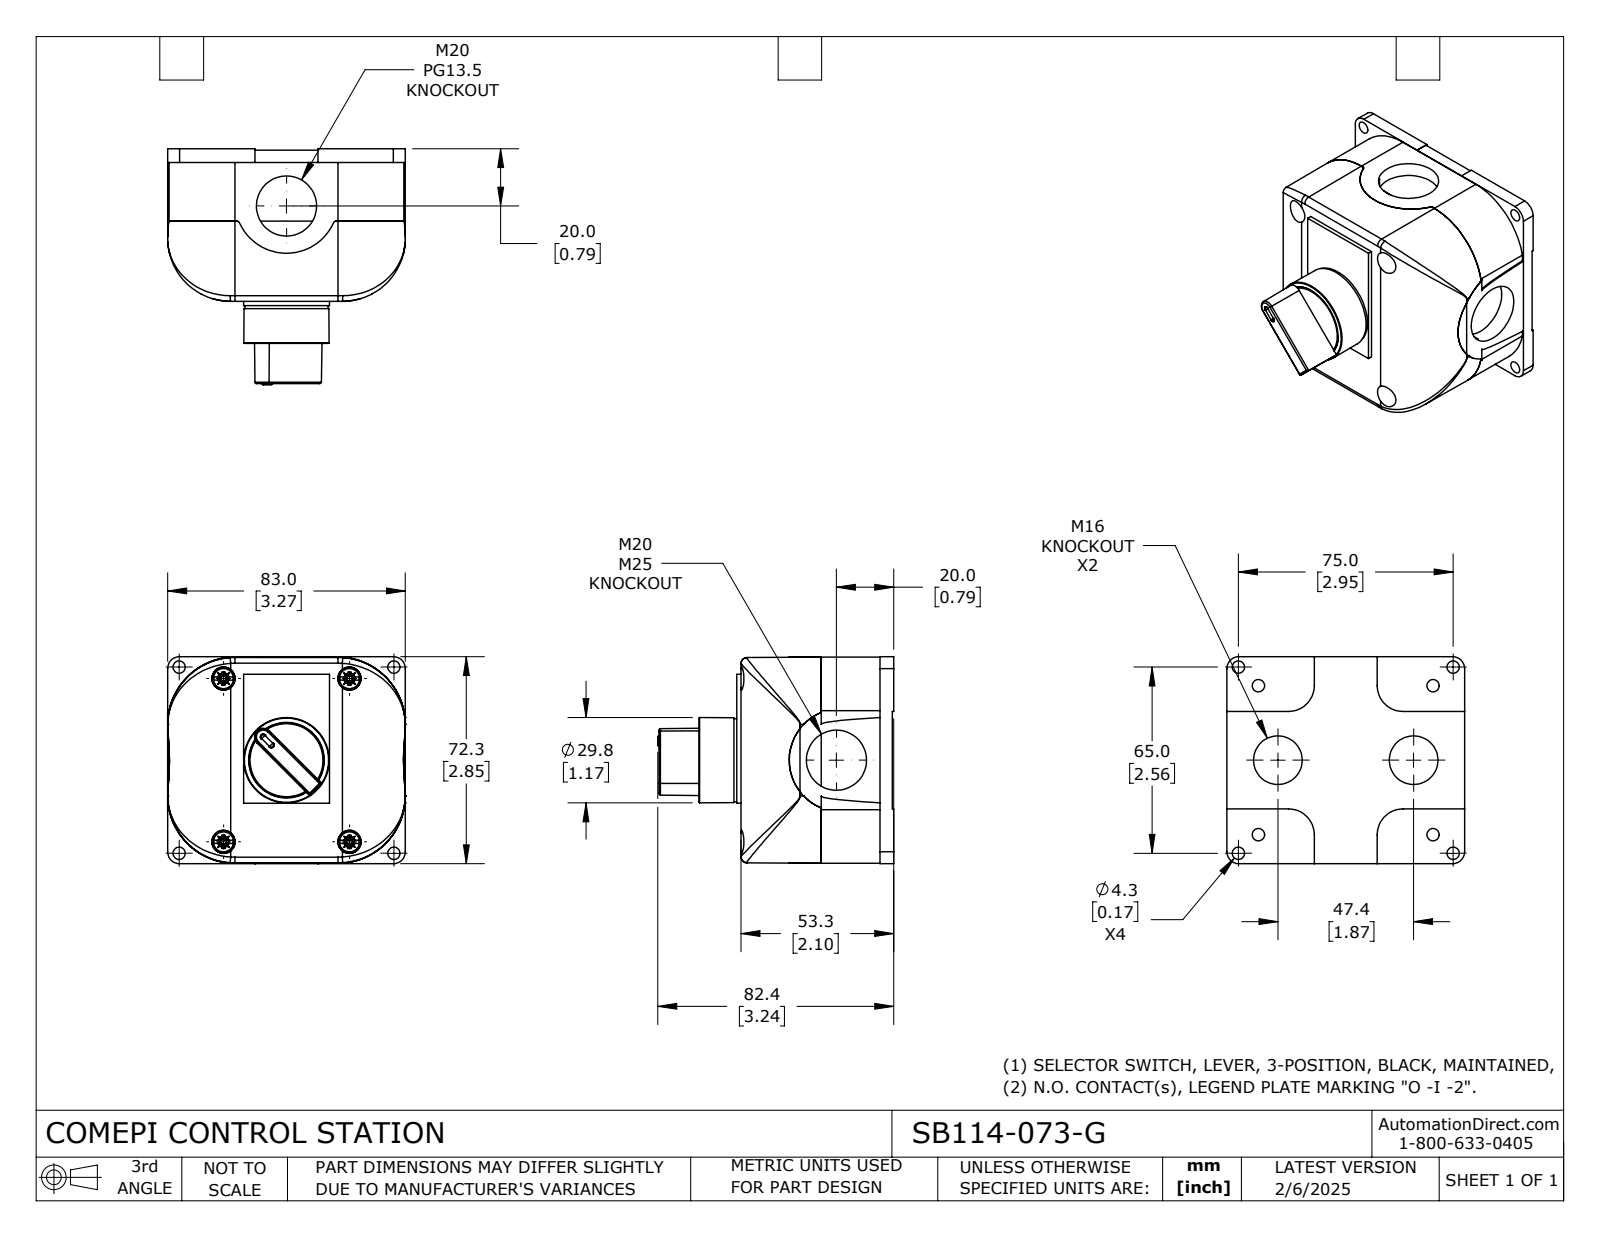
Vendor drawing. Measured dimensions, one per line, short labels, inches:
name: SB114-073-G
written by: SolidWorks 2024 (CONFIG_CONTROL_DESIGN)
unit: in
bodies: 5 solids, 586 faces (332 planar, 159 cylindrical, 95 other)
size: 3.268 × 3.244 × 2.846
volume: 13.1 in³; area: 94.77 in²
holes: 8× ⌀0.169, 4× ⌀0.323, 2× ⌀0.669, 2× ⌀0.827, 1× ⌀0.098, 1× ⌀0.5, 1× ⌀0.551, 1× ⌀0.75, 1× ⌀0.854, 1× ⌀0.886, 1× ⌀0.976, 1× ⌀1.024
bosses: 4× ⌀0.276, 1× ⌀1.142, 1× ⌀1.004, 1× ⌀0.965, 1× ⌀0.85, 1× ⌀0.669, 1× ⌀0.441, 1× ⌀0.343
rounds: 5× R0.039, 4× R0.035, 4× R0.079, 4× R0.354, 4× R0.38, 4× R0.925, 3× R0.02, 2× R0.01
face distances: 2.079, 0.098, 0.976, 1.102, 0.878, 1.98, 0.118, 0.02, 0.996, 2.098
hole spacings: 0.376, 1.058, 1.39, 1.578, 1.954, 2.32, 2.367, 2.689
